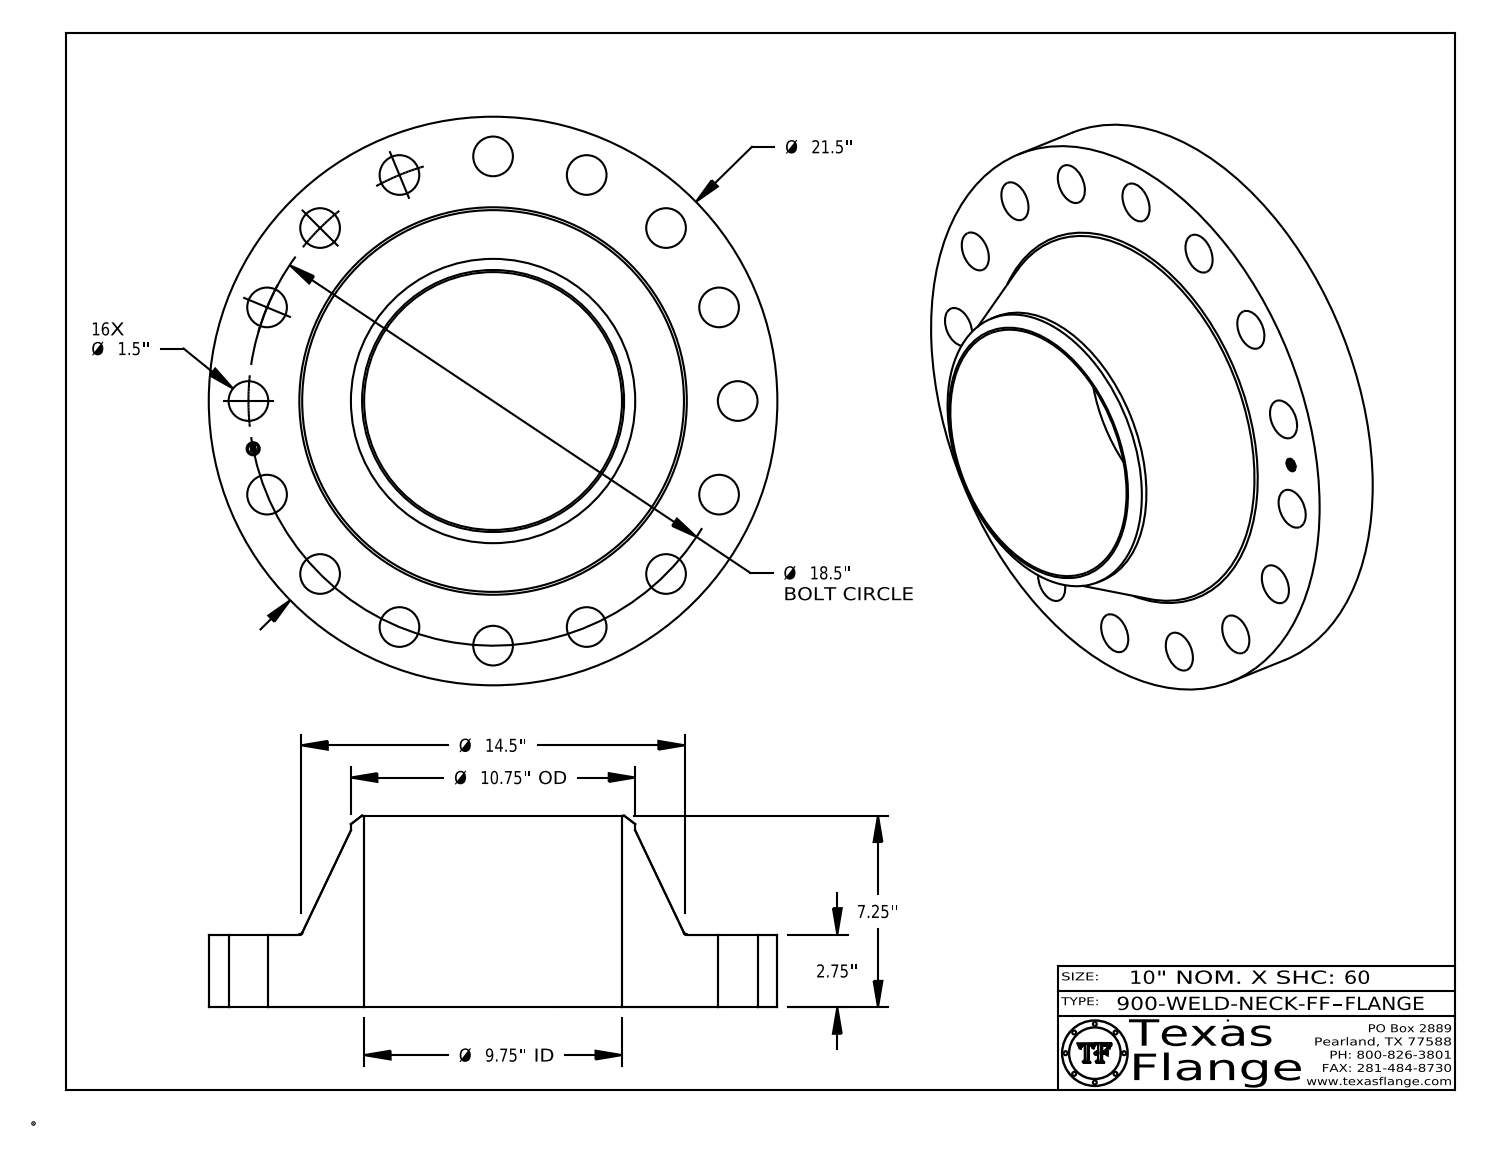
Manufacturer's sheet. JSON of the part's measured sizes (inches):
{"part_name": "900-WELD-NECK-FF", "step_written_by": "CATIA V5 STEP AP214 (AUTOMOTIVE_DESIGN)", "units": "inches", "bodies": {"solids": 1, "faces": 432, "planar": 368, "cylindrical": 58, "other": 6}, "overall_size": [21.5, 21.5, 7.25], "volume_in3": 924.8, "surface_area_in2": 1245, "round_holes": [[1.5, 16], [0.495, 1], [9.75, 1]], "round_bosses_or_shafts": [[0.03, 8], [21.5, 1], [10.75, 1], [0.39, 1]], "face_to_face_distances": [2.75, 7.25, 4.5, 2.735, 0.015, 4.515, 0.148, 0.145, 0.027, 0.096], "hole_center_spacings": [15.382, 7.08, 9.25, 13.081, 3.609, 3.609, 10.278, 10.278]}
